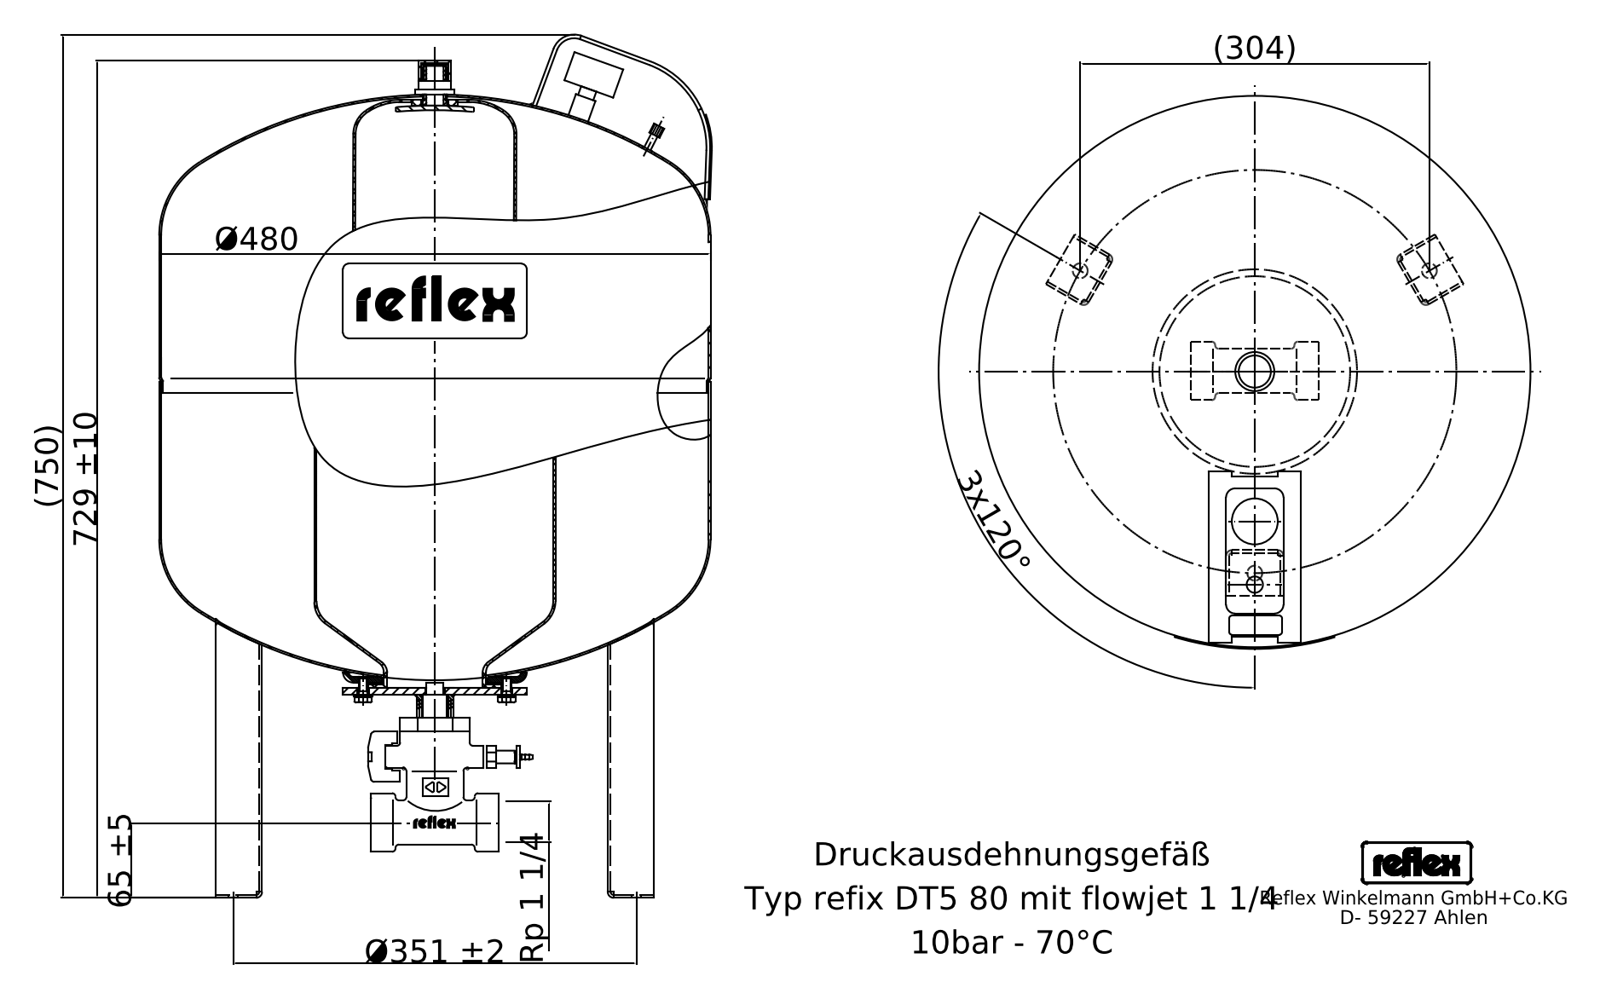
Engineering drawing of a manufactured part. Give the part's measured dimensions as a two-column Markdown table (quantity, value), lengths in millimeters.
| quantity | value |
| --- | --- |
| STEP written by | Mechanical Desktop 2008 (CONFIG_CONTROL_DESIGN) |
| units | millimeters |
| bodies | 21 solids, 683 faces (289 planar, 251 cylindrical, 143 other) |
| overall size | 746.24 × 480 × 480 |
| volume | 76 350 000 mm³ |
| surface area | 2 019 000 mm² |
| round holes (diameter × count) | 13.4 × 3, 2.48 × 1, 3.8 × 1, 4.3 × 1, 4.4 × 1, 5.45 × 1, 7 × 1, 8 × 1, 11.4 × 1, 42.4 × 1, 92 × 1, 150 × 1 |
| round bosses / shafts (diameter × count) | 10 × 9, 18 × 2, 13 × 2, 480 × 1, 160 × 1, 140 × 1, 62 × 1, 56 × 1 |
| partial cylindrical surfaces (radius × count) | 0.5 × 20, 1 × 15, 2.5 × 15, 5 × 15, 3.94 × 4, 1.57 × 3, 2.69 × 2, 4.72 × 2 |
| main face-to-face distances | 240, 2.5, 47.5, 45, 50, 142, 382, 6, 148, 388 |
| hole center spacings | 175.5, 303.98 |
